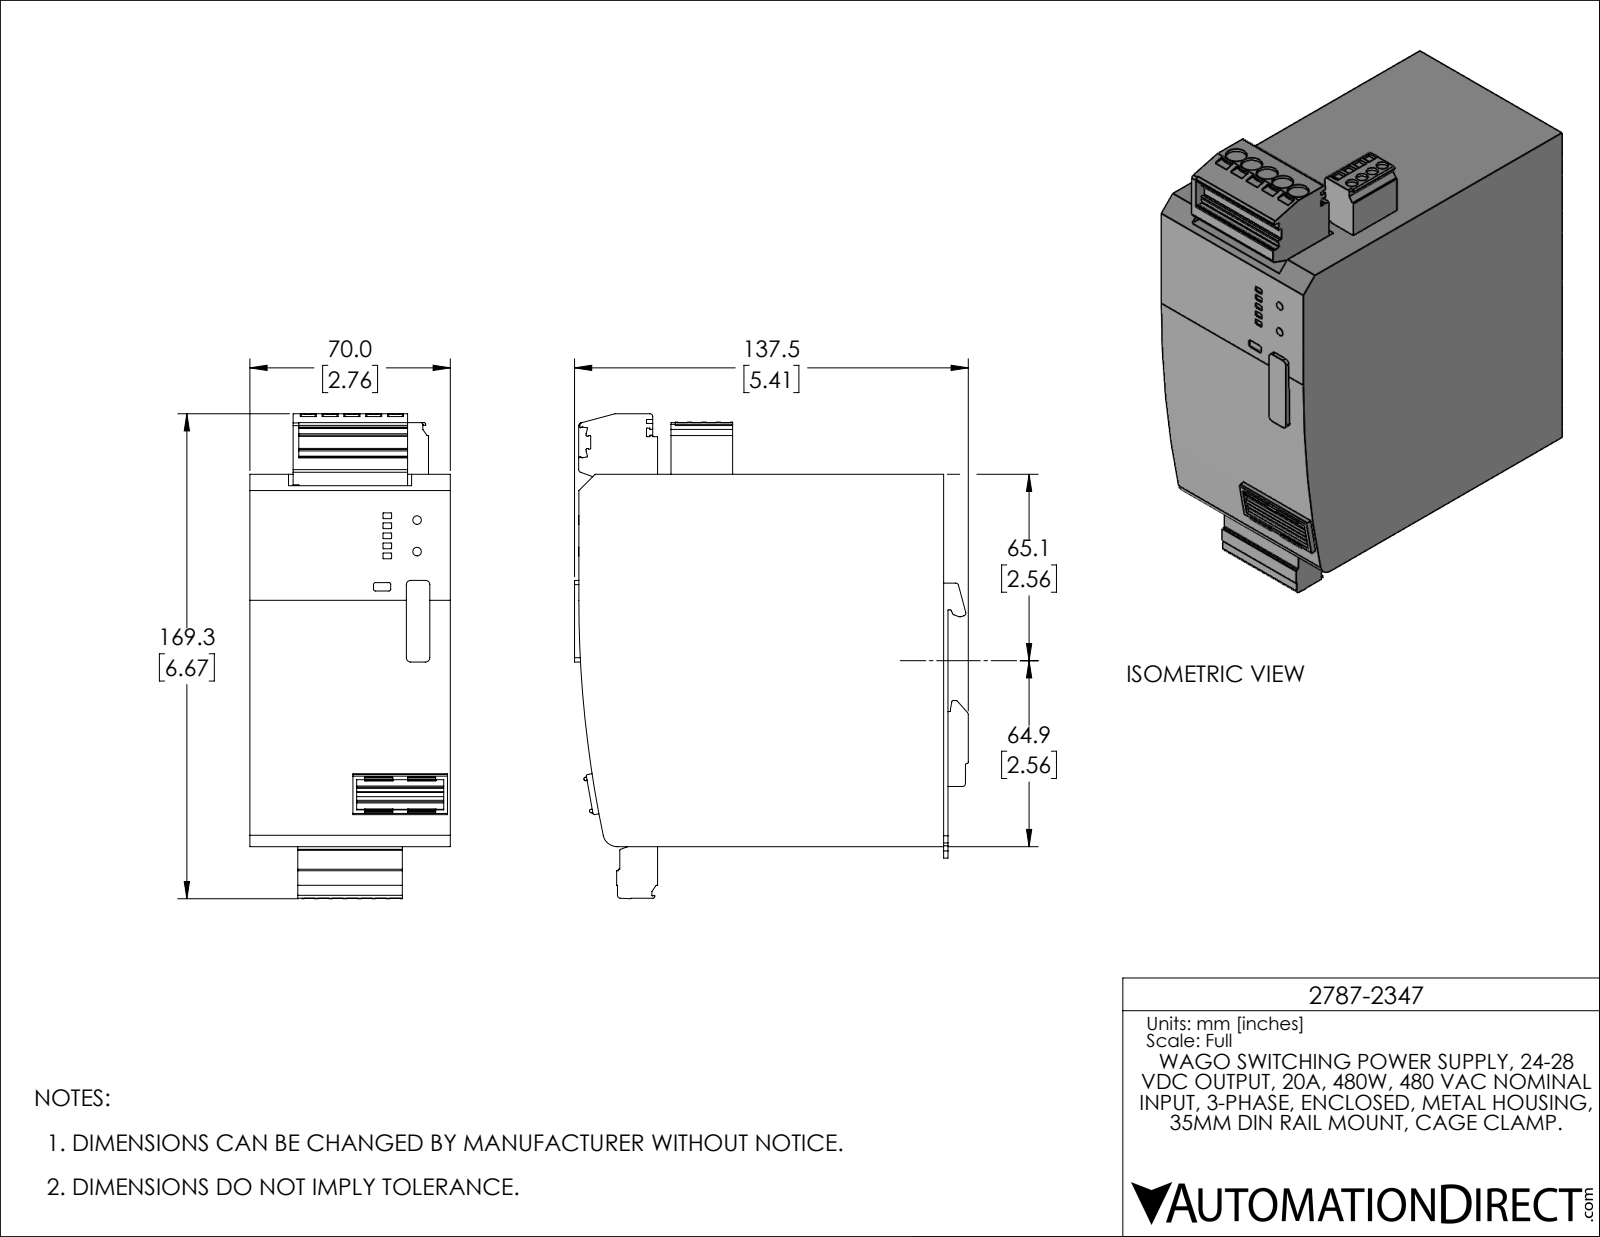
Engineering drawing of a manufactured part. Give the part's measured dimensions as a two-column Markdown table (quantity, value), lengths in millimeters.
| quantity | value |
| --- | --- |
| part name | 2787-2347 |
| STEP written by | SolidWorks 2021 (CONFIG_CONTROL_DESIGN) |
| units | millimeters |
| bodies | 1 solid, 490 faces (322 planar, 168 cylindrical, 0 other) |
| overall size | 169.32 × 137.5 × 70 |
| volume | 1 180 000 mm³ |
| surface area | 78 965 mm² |
| round holes (diameter × count) | 4.2 × 11, 7.5 × 5 |
| round bosses / shafts (diameter × count) | 3 × 2 |
| partial cylindrical surfaces (radius × count) | 0.2 × 39, 1 × 15, 0.5 × 10, 0.6 × 8, 0.3 × 5, 7.6 × 5, 0.4 × 4, 1.5 × 4 |
| main face-to-face distances | 70, 130, 1.5, 128.9, 127.4, 101.4, 99.9, 27.5, 1, 15.1 |
| hole center spacings | 5, 10, 15, 7.62, 15.24, 20, 6.3, 22.86 |
